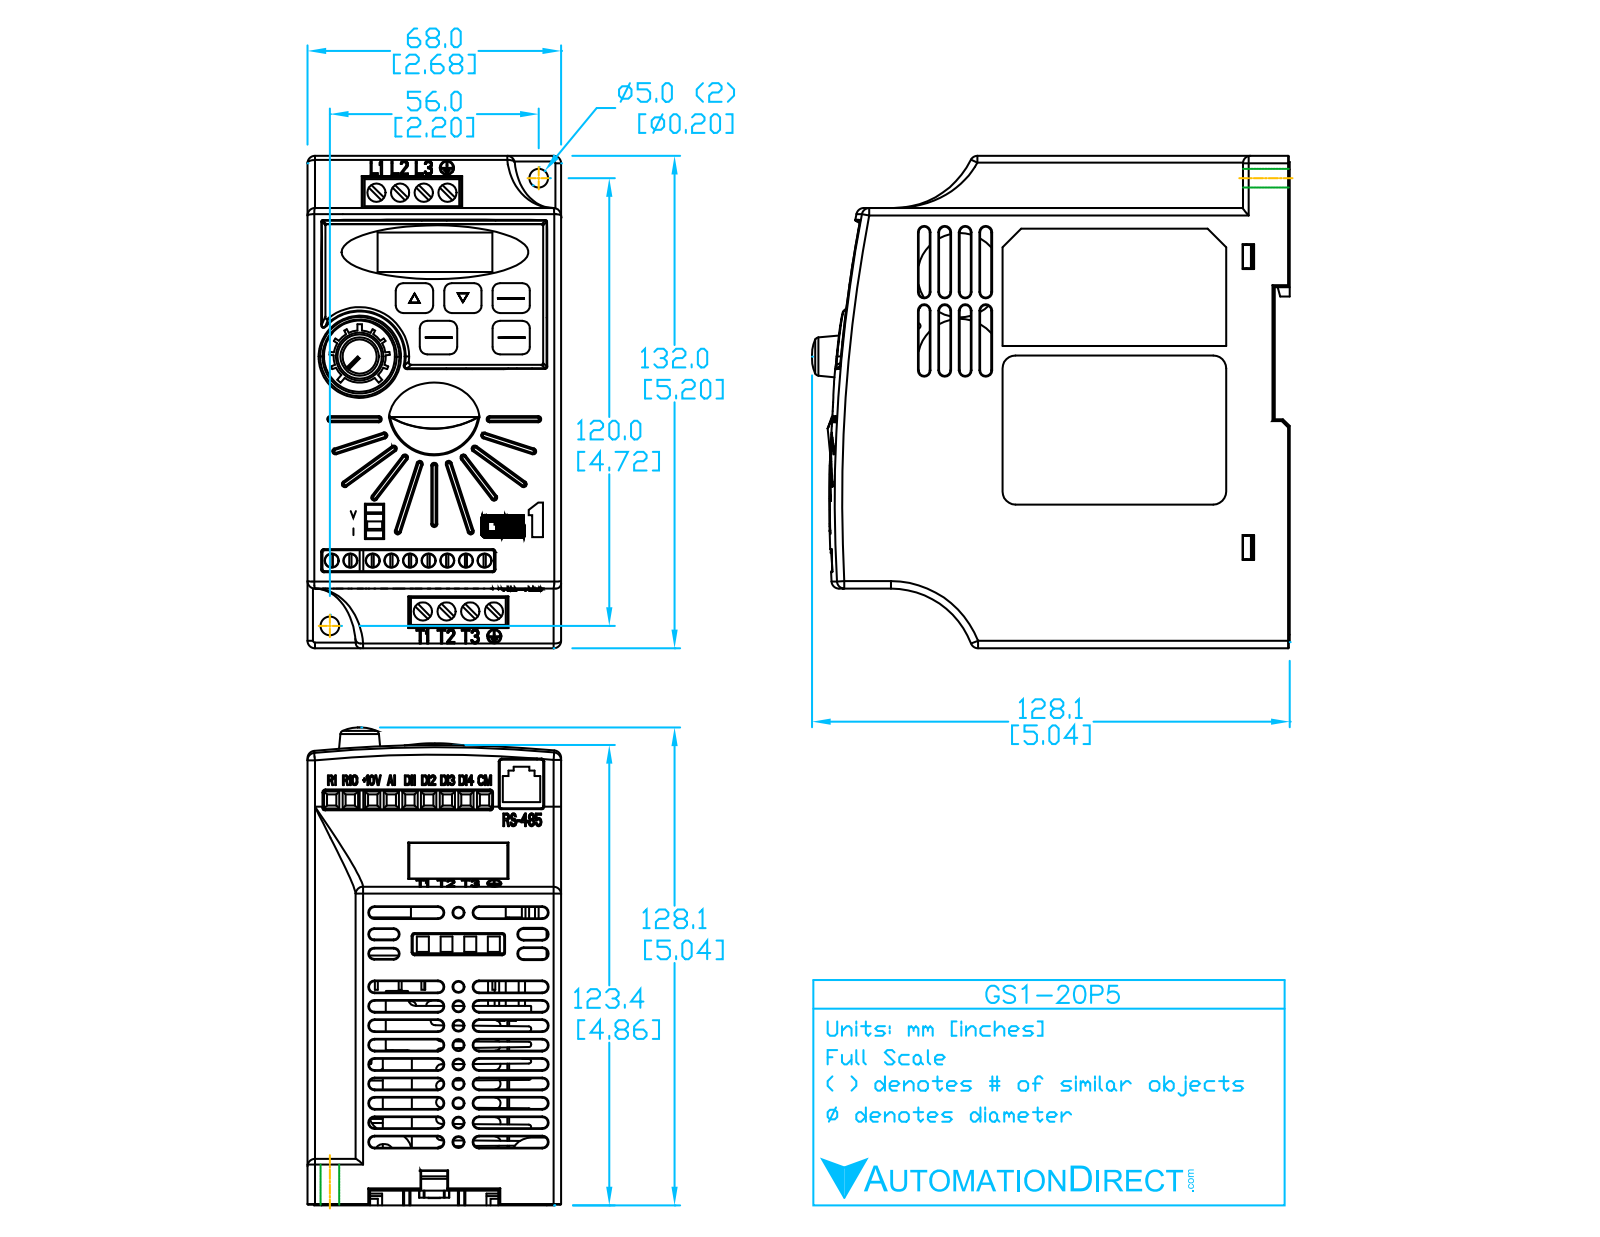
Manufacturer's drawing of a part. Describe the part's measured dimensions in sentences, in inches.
The part is named "GS1-20P5". Its 3-D file was written by "SolidWorks 2013 (AUTOMOTIVE_DESIGN)". It is 1 solid with 902 faces: 559 planar, 168 cylindrical and 175 other. Overall it measures 5.285 by 5.2 by 2.68 inches. Its volume is 61.51 cubic inches and its surface area 109.5 square inches. Round holes: 9 of diameter 0.15, 8 of diameter 0.187, 2 of diameter 0.2. Round bosses or shafts: 5 of diameter 0.316. Partial cylindrical surfaces (rounded edges, fillets, slot ends): 38 of radius 0.03, 22 of radius 0.1, 20 of radius 0.06, 6 of radius 0.063, 2 of radius 0.015, 2 of radius 0.093, 2 of radius 0.2, 2 of radius 0.44. The main face-to-face distances are 2.68, 0.175, 5.2, 0.015, 5.185, 0.167, 0.55, 4.65, 0.535, 0.62. The hole center spacings are 0.2, 0.4, 0.6, 0.8, 1, 1.2, 1.4, 3.921.
